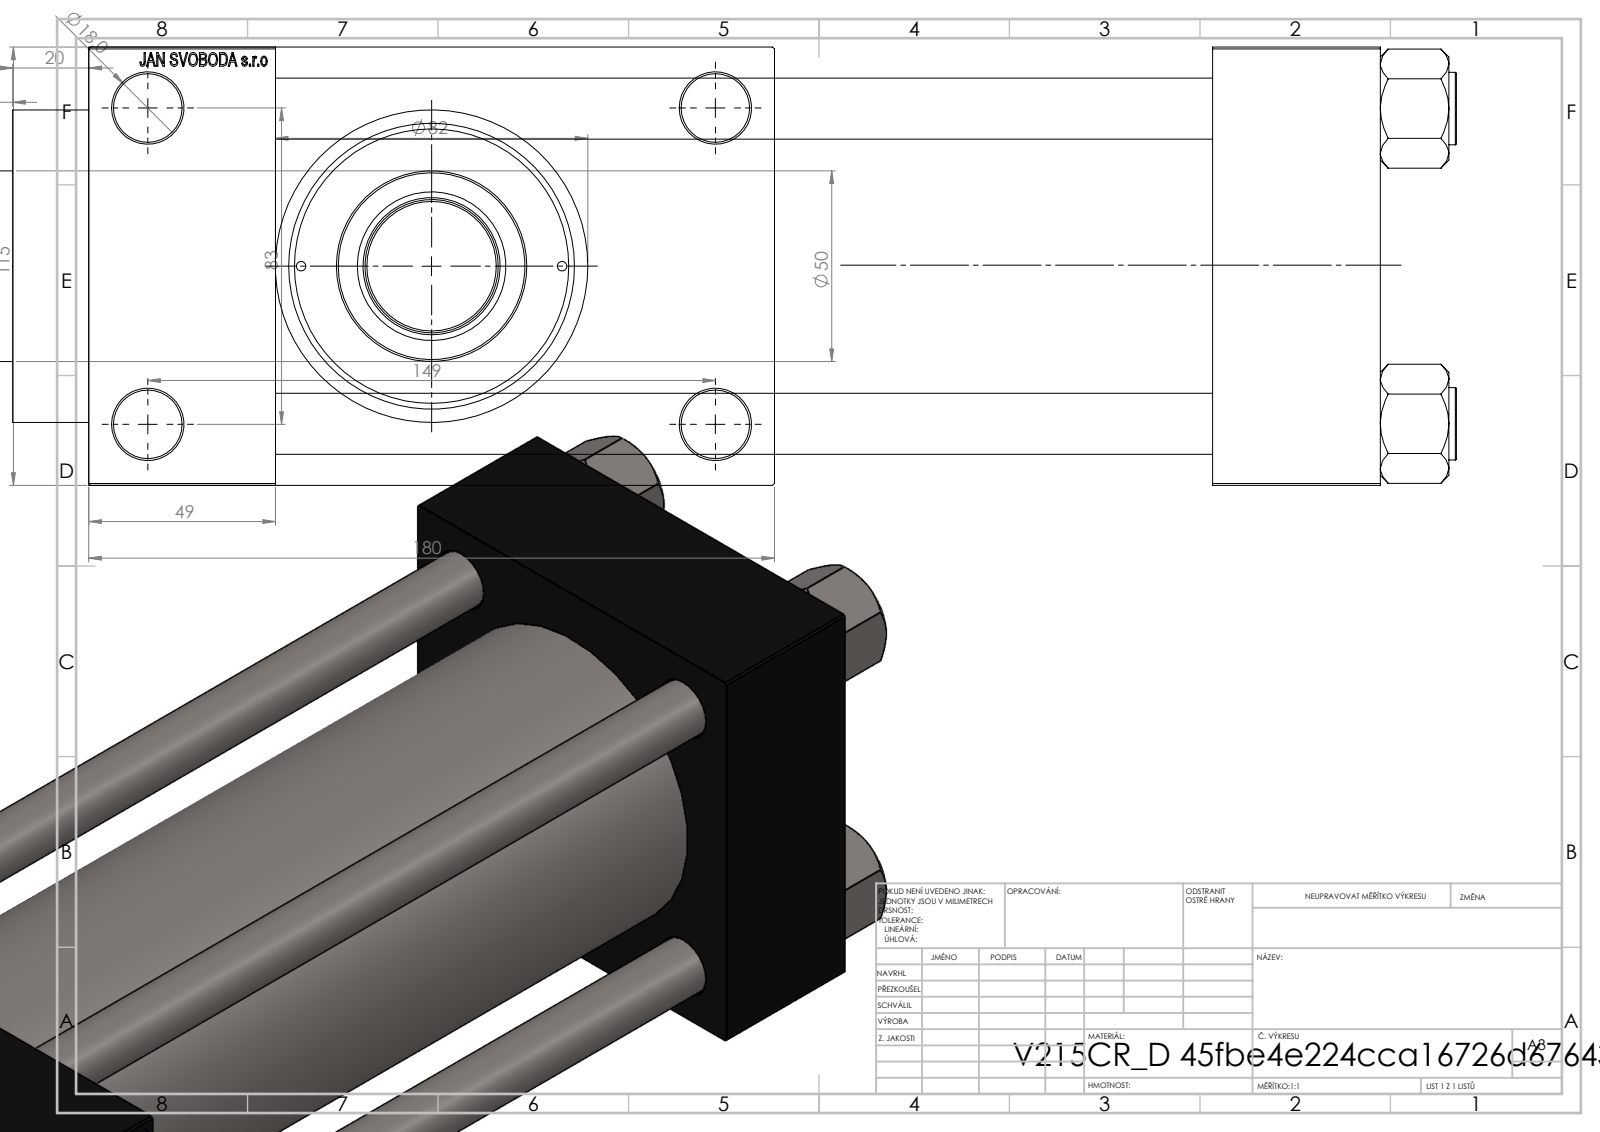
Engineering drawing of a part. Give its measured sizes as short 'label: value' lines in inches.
name: V215CR_VCP_D; V215CR_D_Body; V215CR_ROD_END_F; V215_VC_A (+2 more)
written by: SolidWorks 2019 (CONFIG_CONTROL_DESIGN)
unit: in
bodies: 12 solids, 1174 faces (551 planar, 97 cylindrical, 526 other)
size: 17.559 × 7.087 × 4.528
volume: 151.9 in³; area: 697.1 in²
holes: 4× ⌀0.63, 4× ⌀0.709, 2× ⌀0.098, 2× ⌀0.276, 2× ⌀1.041, 2× ⌀1.378, 1× ⌀1.004, 1× ⌀1.417, 1× ⌀1.535, 1× ⌀2.402, 1× ⌀2.835, 1× ⌀3.15
bosses: 4× ⌀0.748, 1× ⌀3.386, 1× ⌀3.228, 1× ⌀1.969, 1× ⌀1.378, 1× ⌀0.827
face distances: 4.528, 9.685, 1.929, 11.614, 1.732, 11.417, 13.346, 1.28, 5.807, 7.087
hole spacings: 1.305, 1.652, 2.276, 2.302, 3.256, 3.357, 3.393, 3.513
